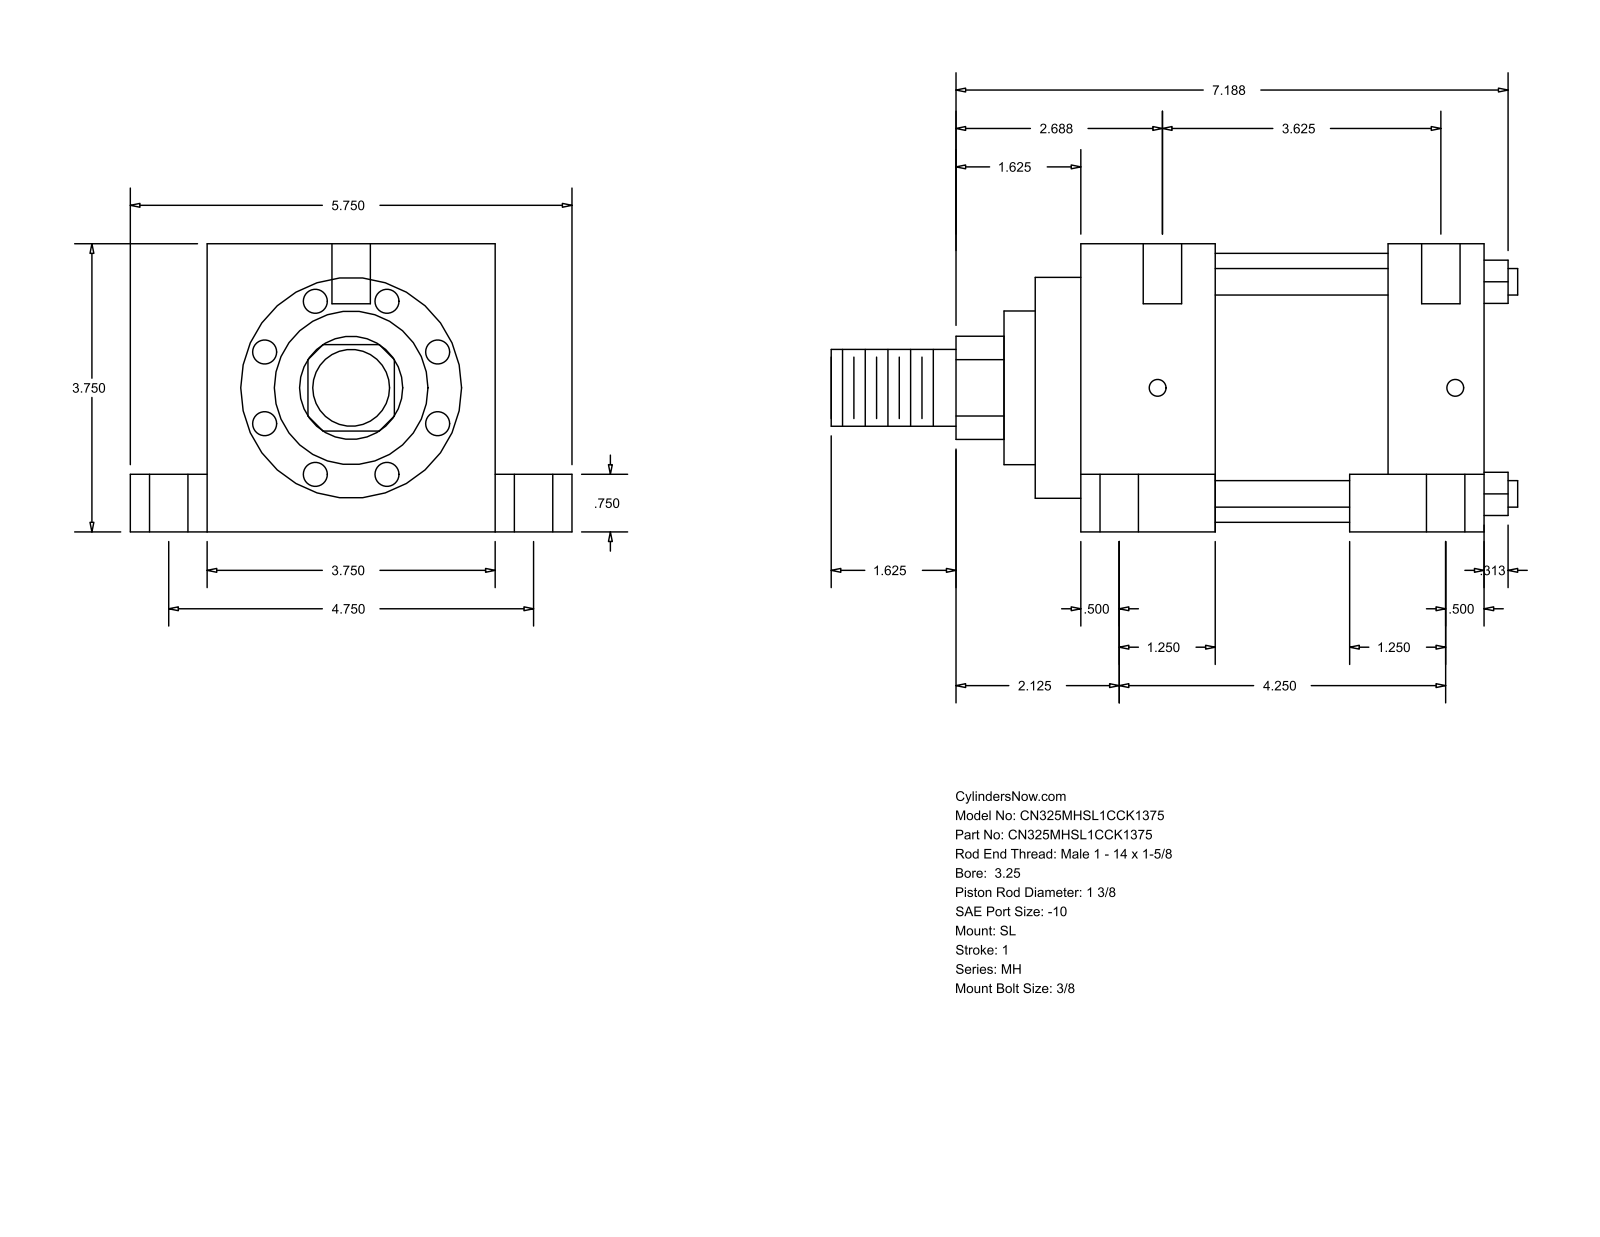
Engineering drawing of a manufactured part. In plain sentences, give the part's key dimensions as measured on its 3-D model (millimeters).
The part is named "MH_SL__0325_1.375". Its 3-D file was written by "GSSL Pune (CONFIG_CONTROL_DESIGN)". It is 0 solids with 110 faces: 77 planar, 33 cylindrical and 0 other. Overall it measures 227.01 by 146.05 by 95.25 millimeters. Round holes: 6 of diameter 12.7, 4 of diameter 5.56, 4 of diameter 19.05. Round bosses or shafts: 4 of diameter 8.76, 1 of diameter 88.9, 1 of diameter 73.03, 1 of diameter 50.8, 1 of diameter 34.92, 1 of diameter 25.4. Partial cylindrical surfaces (rounded edges, fillets, slot ends): 1 of radius 17.06. The main face-to-face distances are 95.24, 133.35, 44.45, 88.9, 25.41, 120.65, 19.05, 76.19, 101.61, 57.16. The hole center spacings are 60.35, 60.41, 61.65, 62, 98.43, 107.95, 111.42, 112.76.
